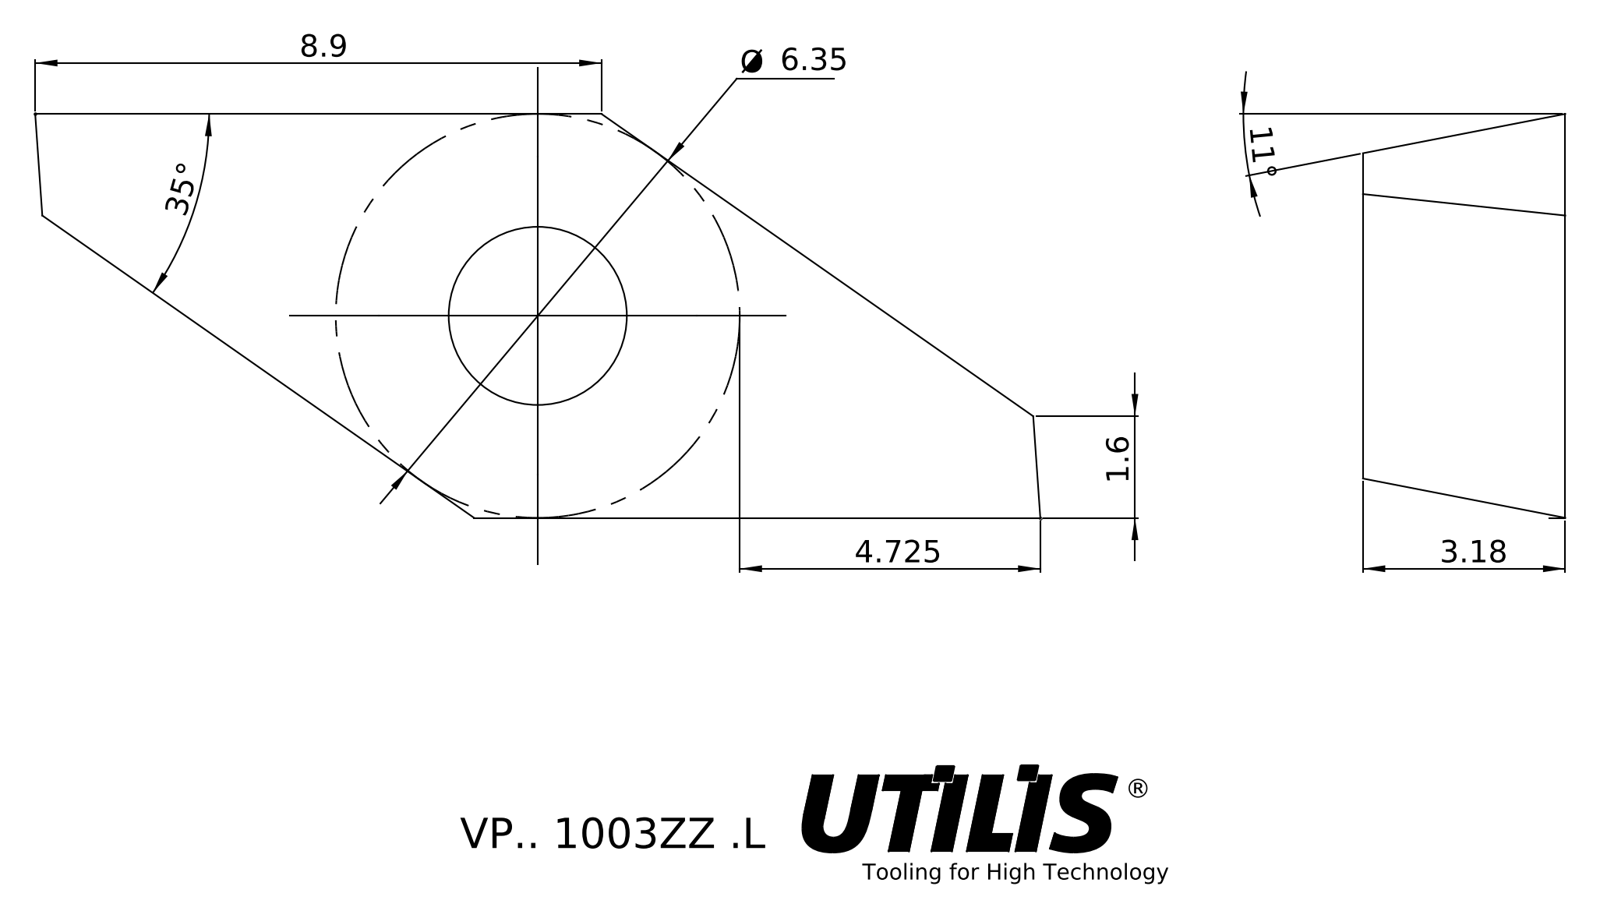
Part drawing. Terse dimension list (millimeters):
name: VP.. 1003ZZ .L
written by: SolidWorks 2016 (AUTOMOTIVE_DESIGN)
unit: mm
bodies: 1 solid, 10 faces (8 planar, 2 cylindrical, 0 other)
size: 15.8 × 6.35 × 3.18
volume: 158 mm³; area: 242 mm²
holes: 1× ⌀2.8
face distances: 3.18
